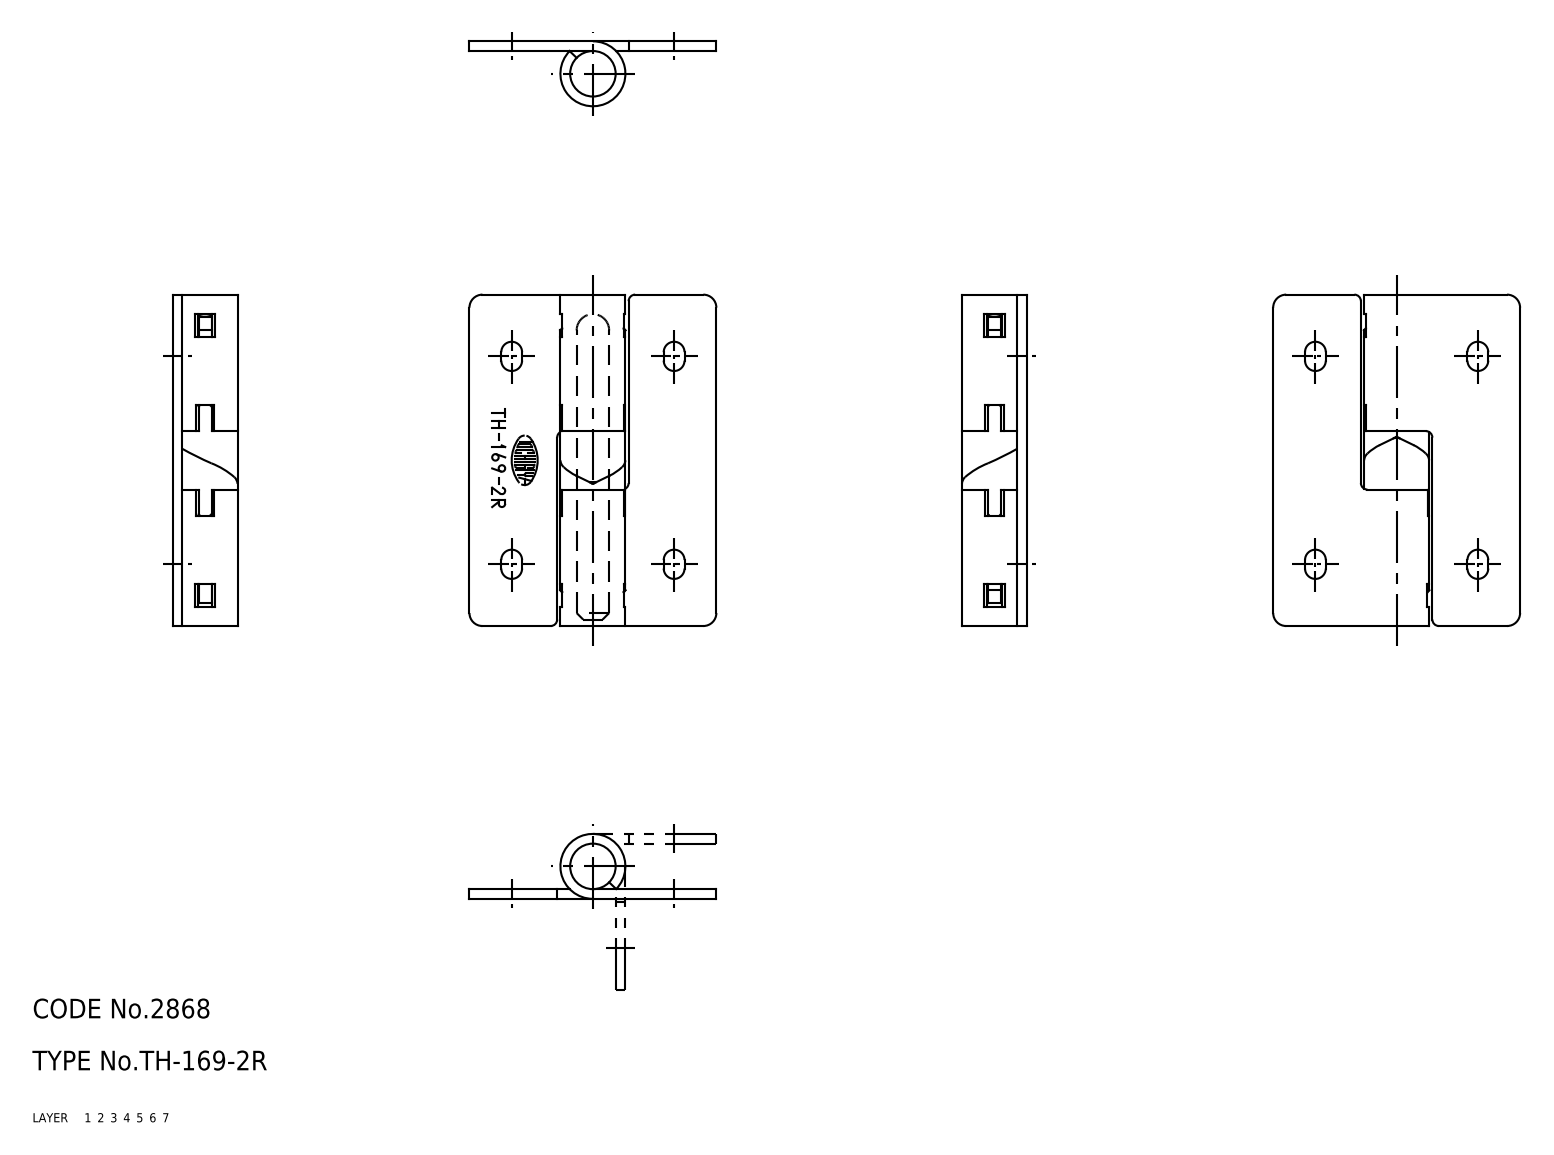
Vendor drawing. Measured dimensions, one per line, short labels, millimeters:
name: 67119660; 67119673
written by: CADfix (AUTOMOTIVE_DESIGN)
unit: mm
bodies: 2 solids, 198 faces (0 planar, 0 cylindrical, 198 other)
size: 51 × 38 × 10
volume: 6 052 mm³; area: 6 617 mm²
